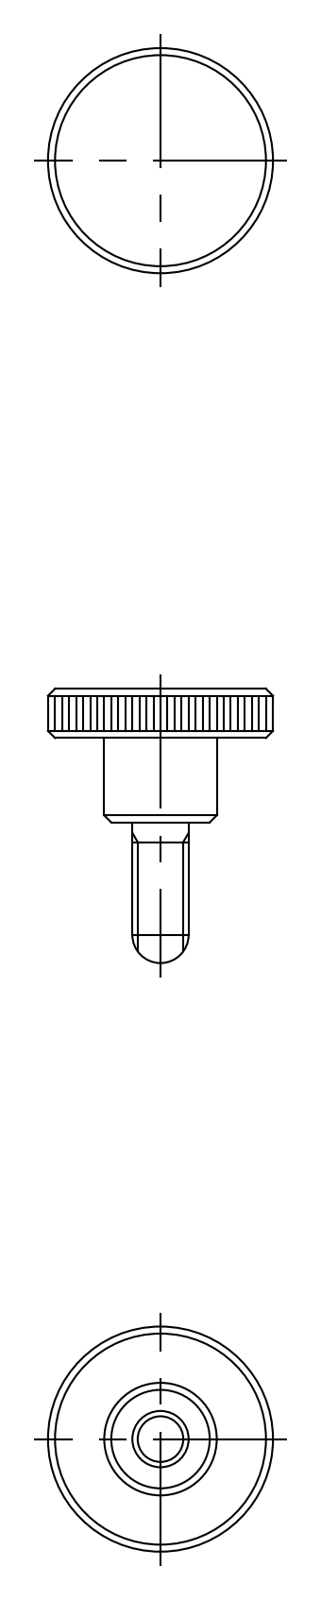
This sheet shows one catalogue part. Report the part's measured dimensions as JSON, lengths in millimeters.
{"part_name": "knob", "step_written_by": "CADfix (AUTOMOTIVE_DESIGN)", "units": "millimeters", "bodies": {"solids": 1, "faces": 16, "planar": 0, "cylindrical": 0, "other": 16}, "overall_size": [19.5, 16, 16], "volume_mm3": 1109, "surface_area_mm2": 804}
